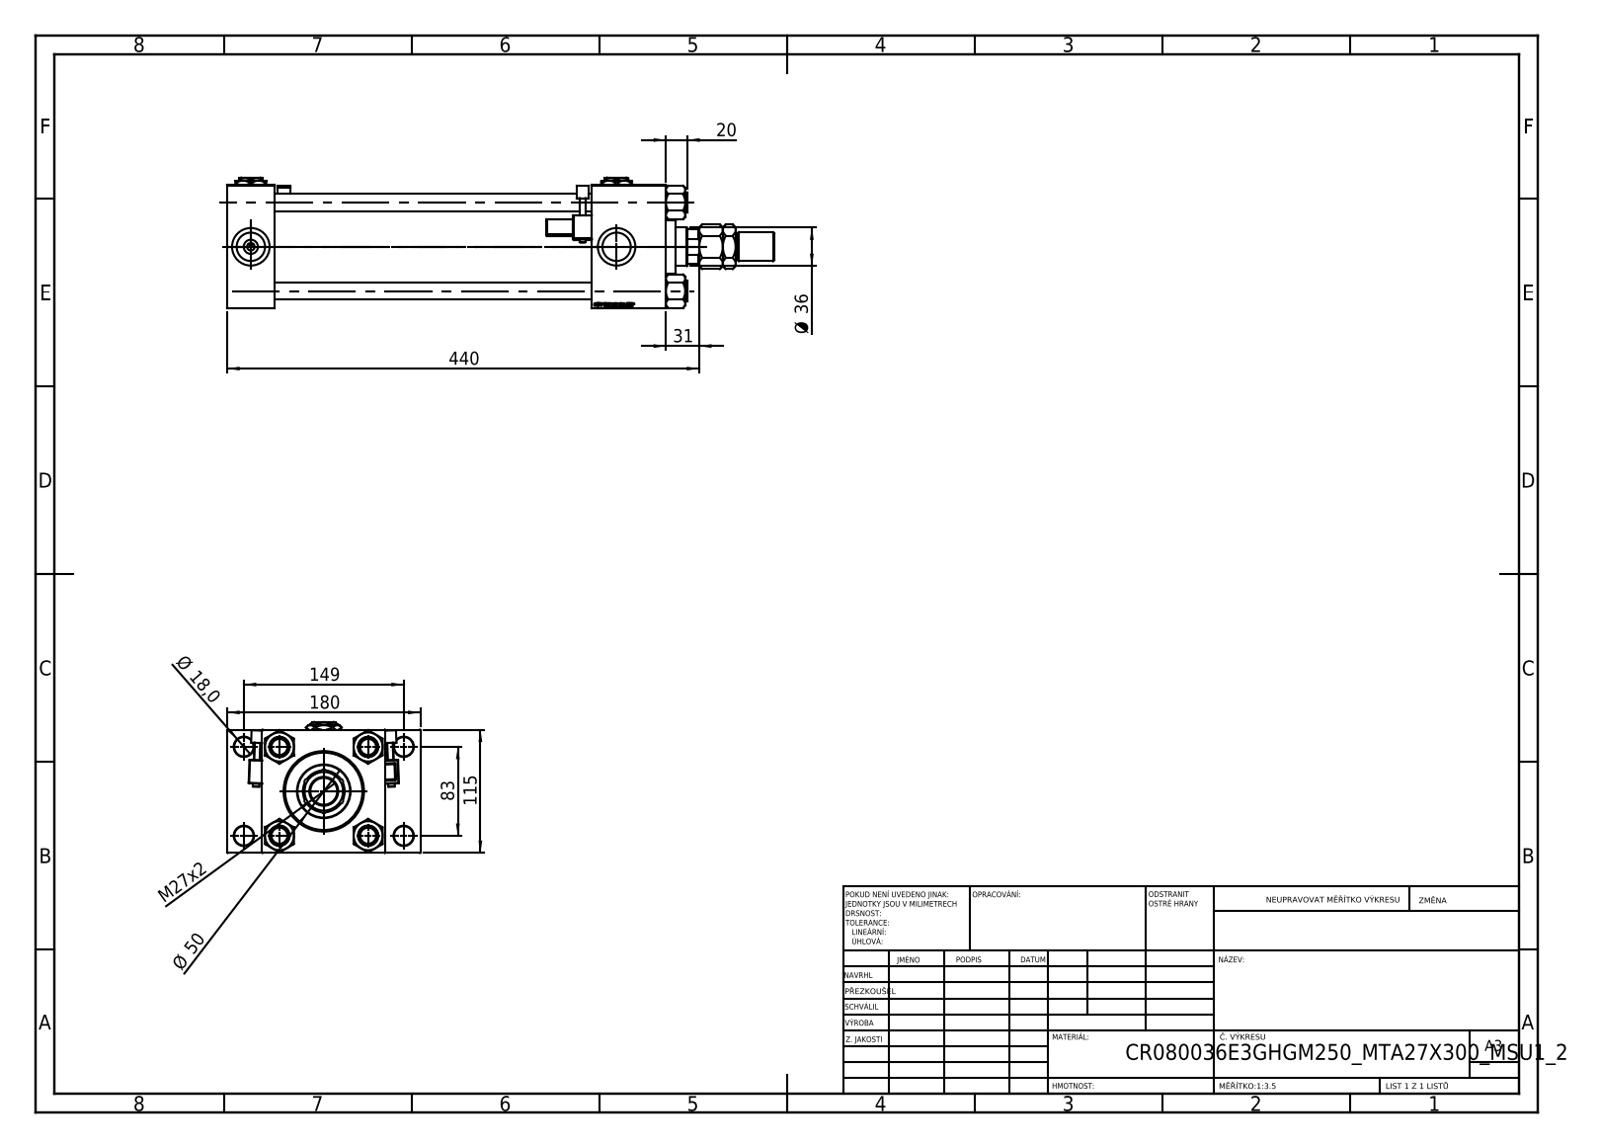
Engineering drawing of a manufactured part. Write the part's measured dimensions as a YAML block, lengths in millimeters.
part_name: "V215CR_E_Body; Zatka_pro_OIL_PORT; MTA; NUT_M5_E (+4 more)"
step_written_by: "SolidWorks 2019 (CONFIG_CONTROL_DESIGN)"
units: millimeters
bodies: {solids: 16, faces: 1487, planar: 666, cylindrical: 161, other: 660}
overall_size: [510, 180, 122]
volume: 2768000
surface_area: 531433
round_holes:
  - {diameter: 16, count: 4}
  - {diameter: 18, count: 4}
  - {diameter: 26.44, count: 4}
  - {diameter: 35, count: 4}
  - {diameter: 7, count: 3}
  - {diameter: 25.5, count: 1}
  - {diameter: 36, count: 1}
  - {diameter: 39, count: 1}
  - {diameter: 61, count: 1}
  - {diameter: 72, count: 1}
  - {diameter: 80, count: 1}
round_bosses_or_shafts:
  - {diameter: 19, count: 4}
  - {diameter: 6, count: 2}
  - {diameter: 86, count: 1}
  - {diameter: 50, count: 1}
  - {diameter: 27, count: 1}
  - {diameter: 25, count: 1}
partial_cylinders:
  - {radius: 0.5, count: 48}
  - {radius: 1, count: 2}
  - {radius: 2.5, count: 2}
  - {radius: 4, count: 2}
  - {radius: 17.5, count: 1}
face_to_face_distances: [115, 44, 409, 365, 32.5, 340, 296, 69, 147.5, 90]
hole_center_spacings: [33.15, 58.48, 82.7, 85.28, 89.24, 115.85, 142.43, 83]
